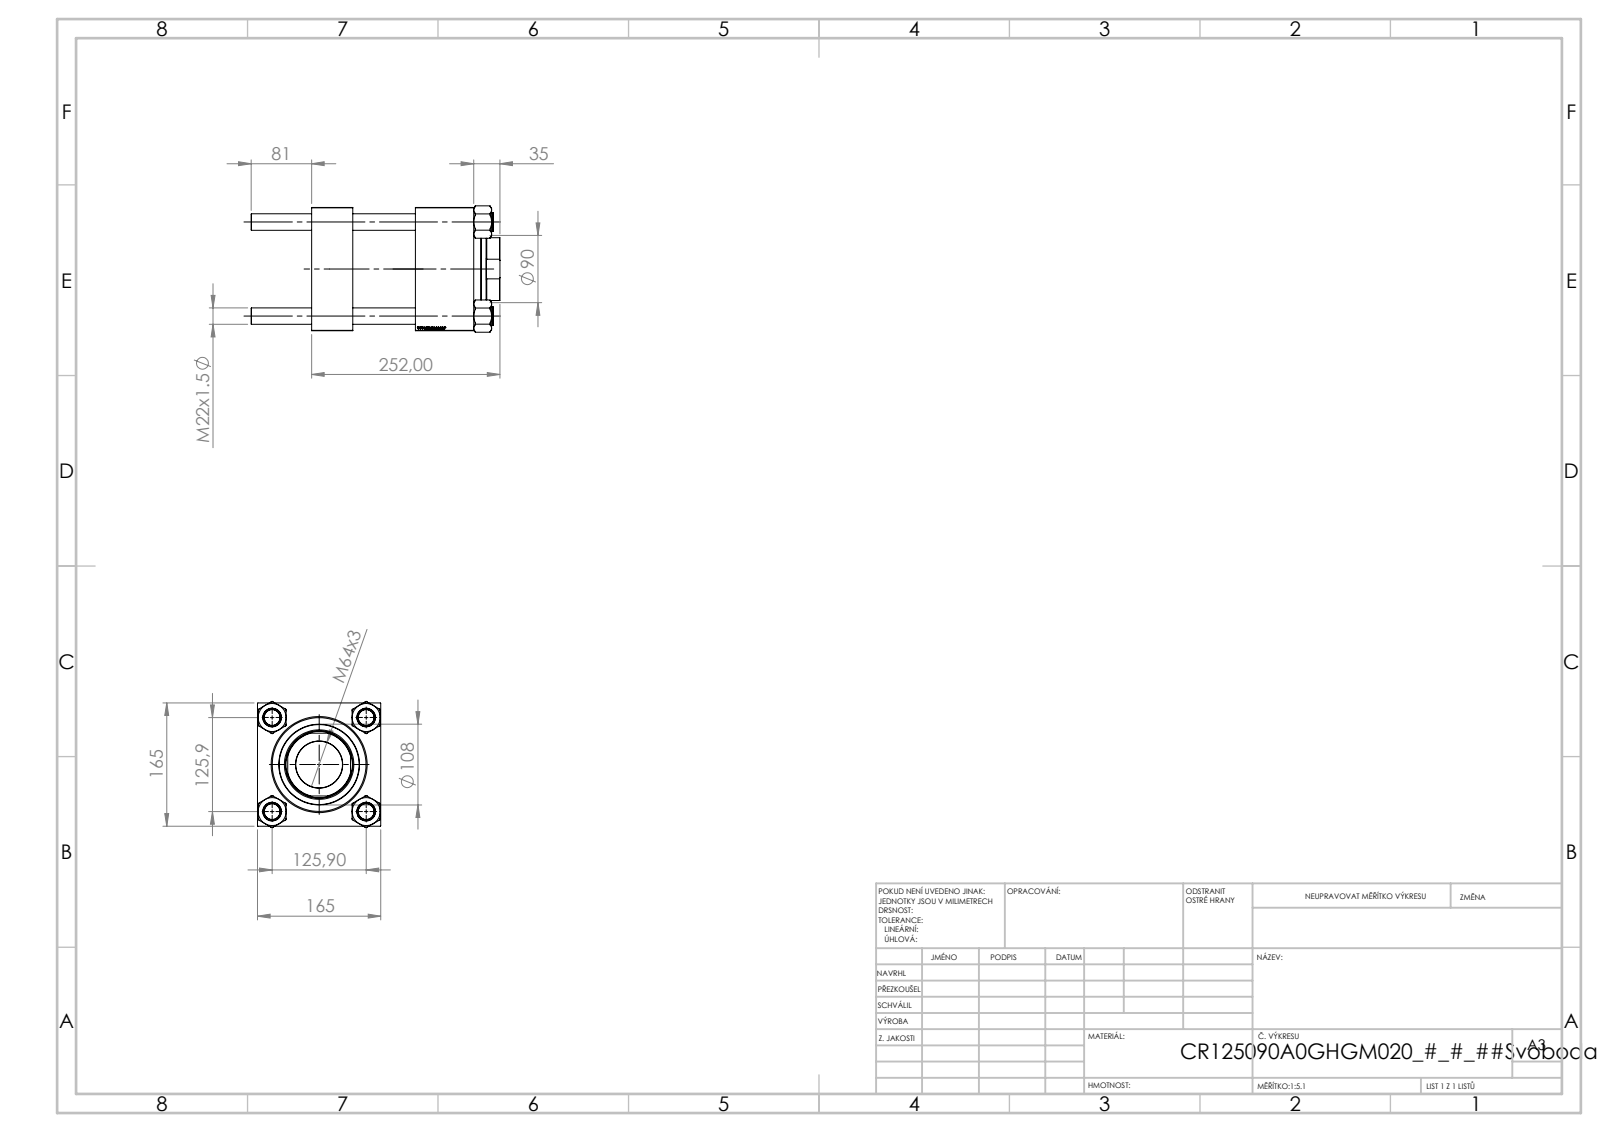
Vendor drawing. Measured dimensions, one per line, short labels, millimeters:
name: V215CR_VCP; V215CR_BODY_A; CR025_012_A_0_G_A_G_M_020_+#_##_TYCINKA; NUT_M5 (+1 more)
written by: SolidWorks 2019 (CONFIG_CONTROL_DESIGN)
unit: mm
bodies: 11 solids, 1182 faces (568 planar, 78 cylindrical, 536 other)
size: 333 × 169.14 × 165
volume: 4 884 000 mm³; area: 570 378 mm²
holes: 4× ⌀22, 2× ⌀7, 2× ⌀32.24, 2× ⌀45, 1× ⌀62.5, 1× ⌀90, 1× ⌀93, 1× ⌀96, 1× ⌀125, 1× ⌀125.5
bosses: 4× ⌀25, 1× ⌀131, 1× ⌀108
rounds: 1× R44
face distances: 165, 55, 162, 217, 84, 139, 78, 188.3, 133.3, 49.3
hole spacings: 89.02, 125.9, 178.05, 138.5
